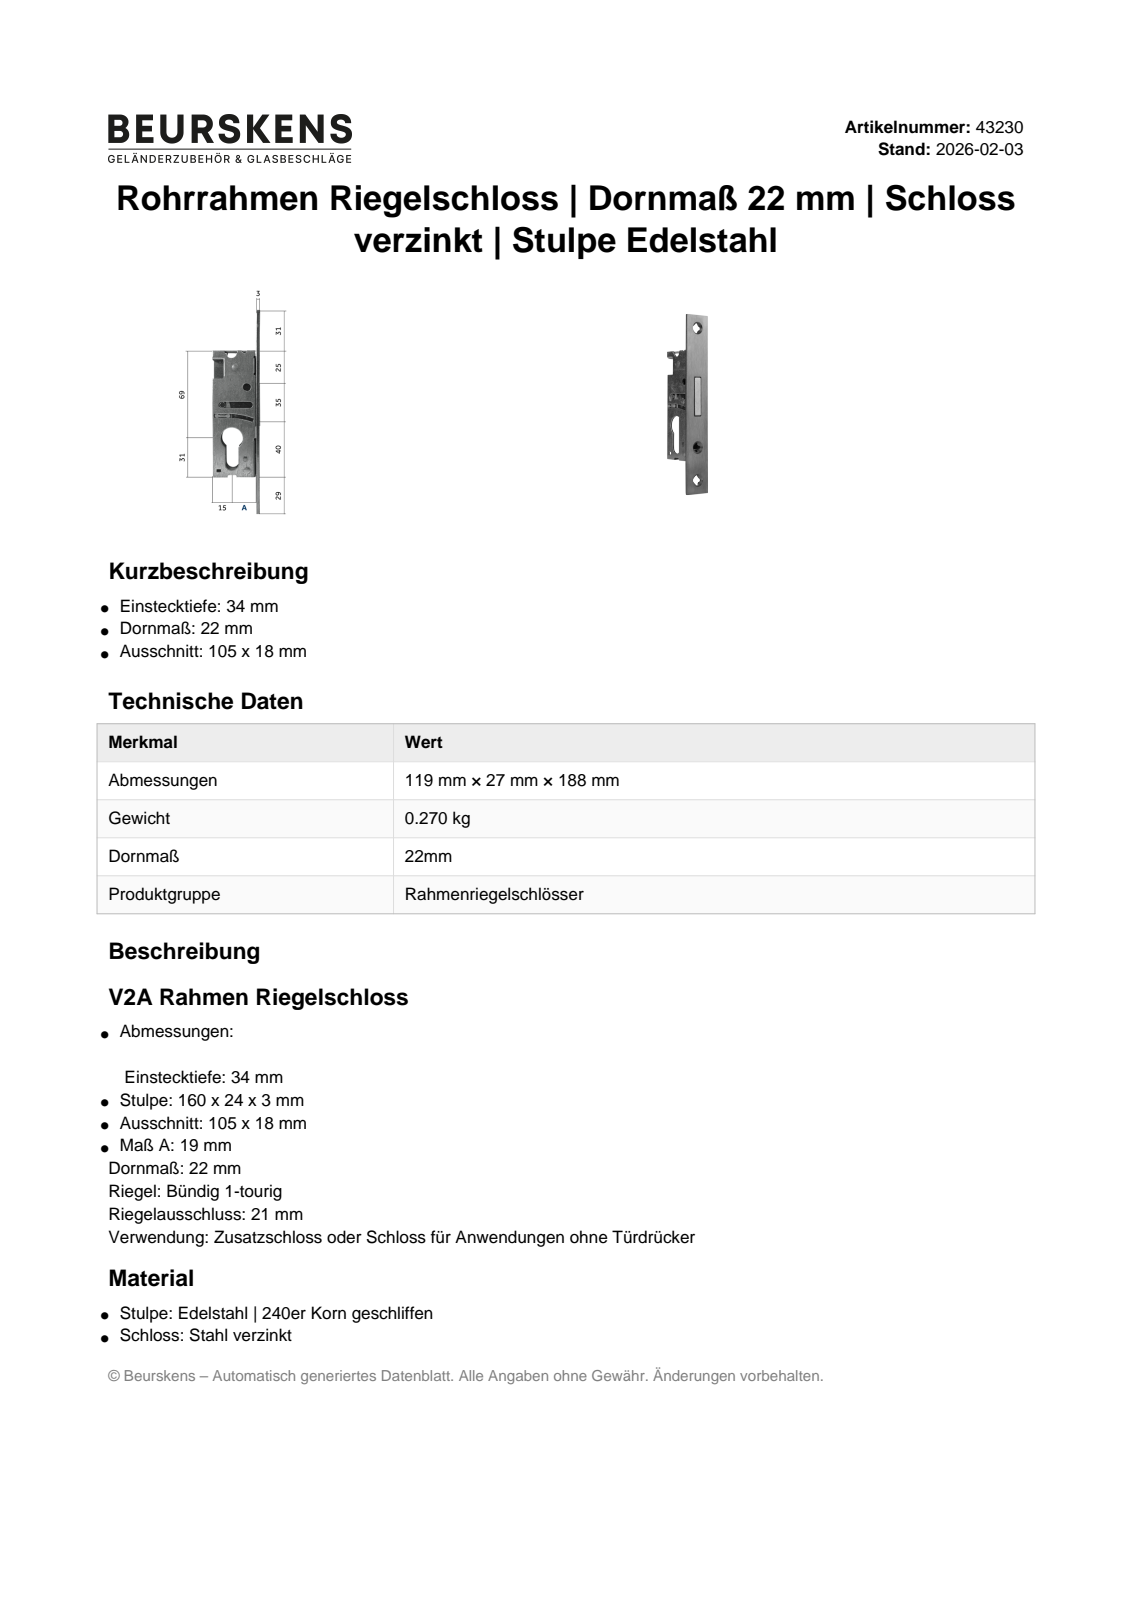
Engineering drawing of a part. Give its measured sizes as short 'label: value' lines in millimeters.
name: 43230
written by: Autodesk Inventor 2022 (AUTOMOTIVE_DESIGN)
unit: mm
bodies: 1 solid, 26 faces (18 planar, 5 cylindrical, 3 other)
size: 160 × 58 × 24
volume: 71 523 mm³; area: 19 585 mm²
holes: 3× ⌀5, 1× ⌀17.5
rounds: 1× R5.25
face distances: 18, 3, 37, 34, 4.5, 13.5, 21, 7.5, 16.5, 24
hole spacings: 35.75, 100.25, 136
